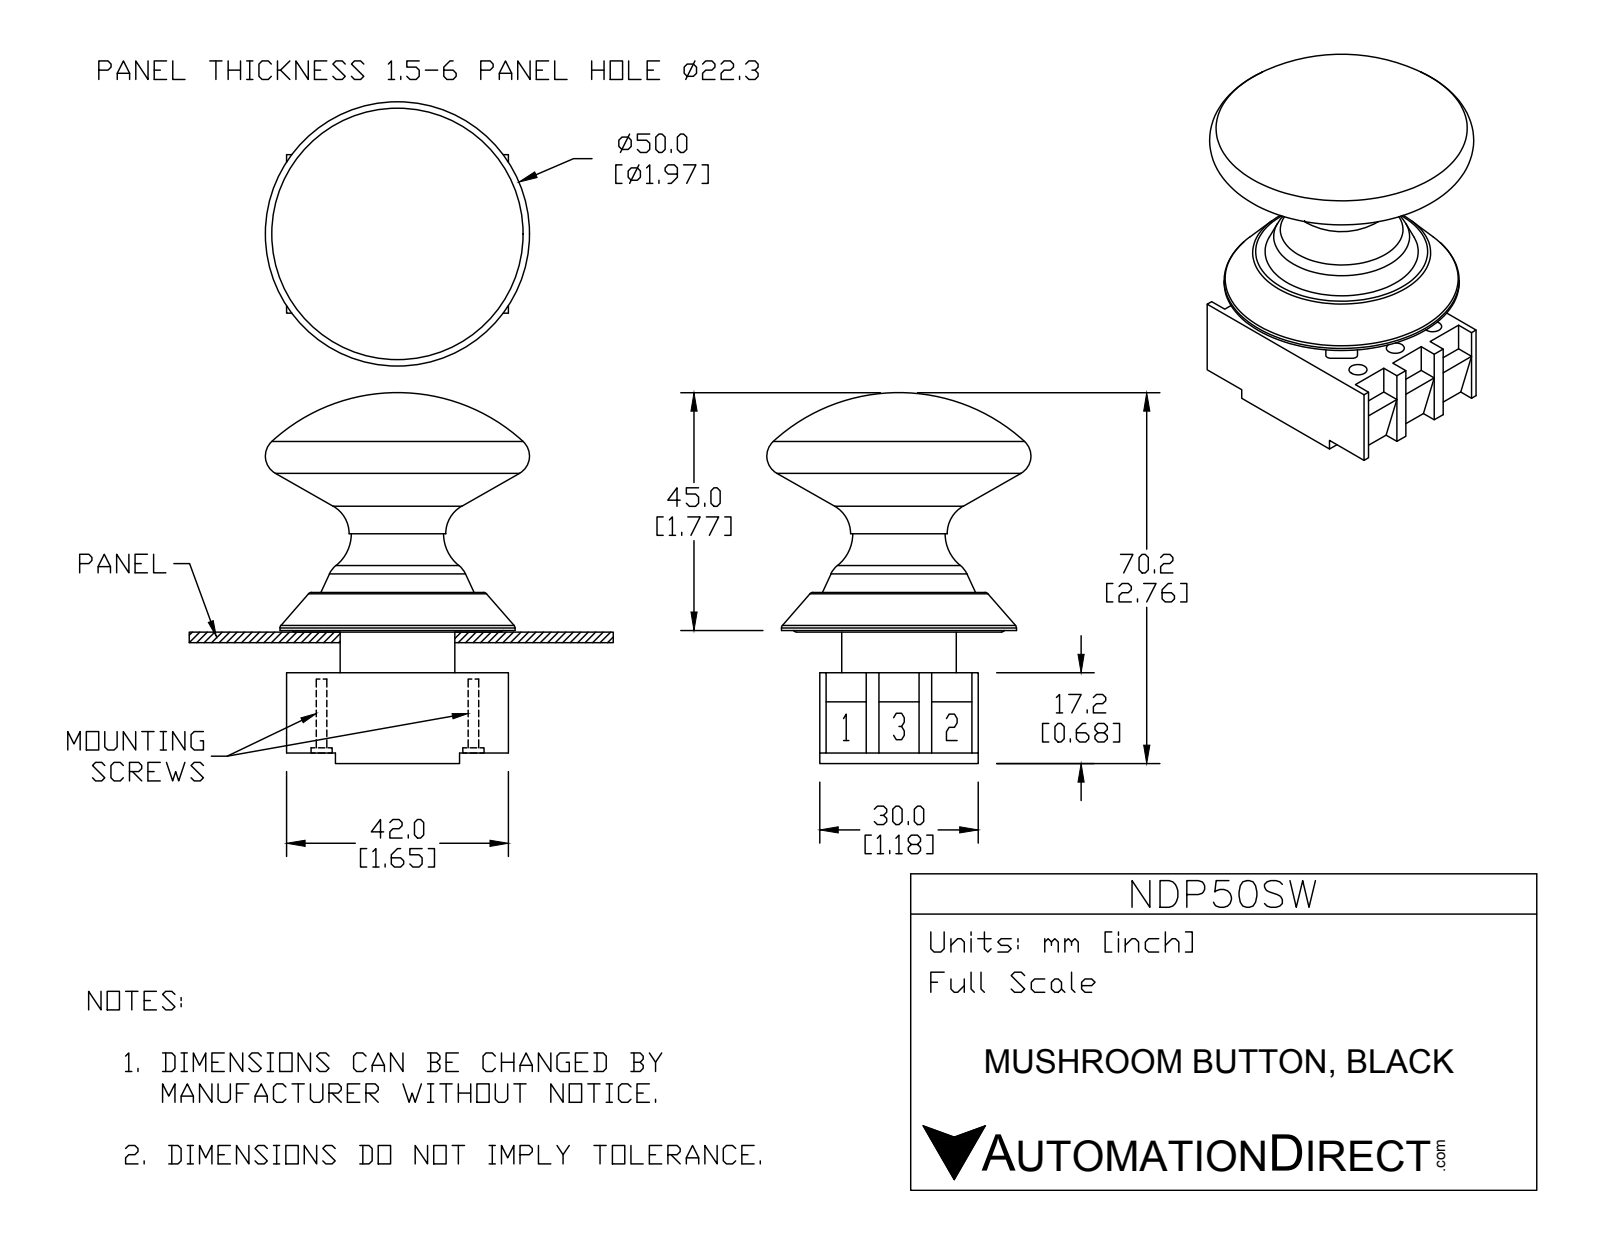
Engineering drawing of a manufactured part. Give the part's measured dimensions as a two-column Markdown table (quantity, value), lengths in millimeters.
| quantity | value |
| --- | --- |
| part name | NDP50SW |
| STEP written by | SolidWorks 2015 (AUTOMOTIVE_DESIGN) |
| units | millimeters |
| bodies | 7 solids, 222 faces (126 planar, 63 cylindrical, 33 other) |
| overall size | 70.2 × 50 × 50 |
| volume | 55 695 mm³ |
| surface area | 21 605 mm² |
| round holes (diameter × count) | 3.4 × 6, 5 × 6, 12.5 × 1 |
| round bosses / shafts (diameter × count) | 4.6 × 2, 4 × 2, 44.5 × 1, 21.7 × 1 |
| partial cylindrical surfaces (radius × count) | 1 × 8, 8.7 × 5, 11 × 1 |
| main face-to-face distances | 7.2, 15.2, 30, 8, 7.5, 7.7, 22.9, 10, 23.2, 30.4 |
| hole center spacings | 10, 17.52, 30.45, 28.76, 14.38, 20, 35.03 |
